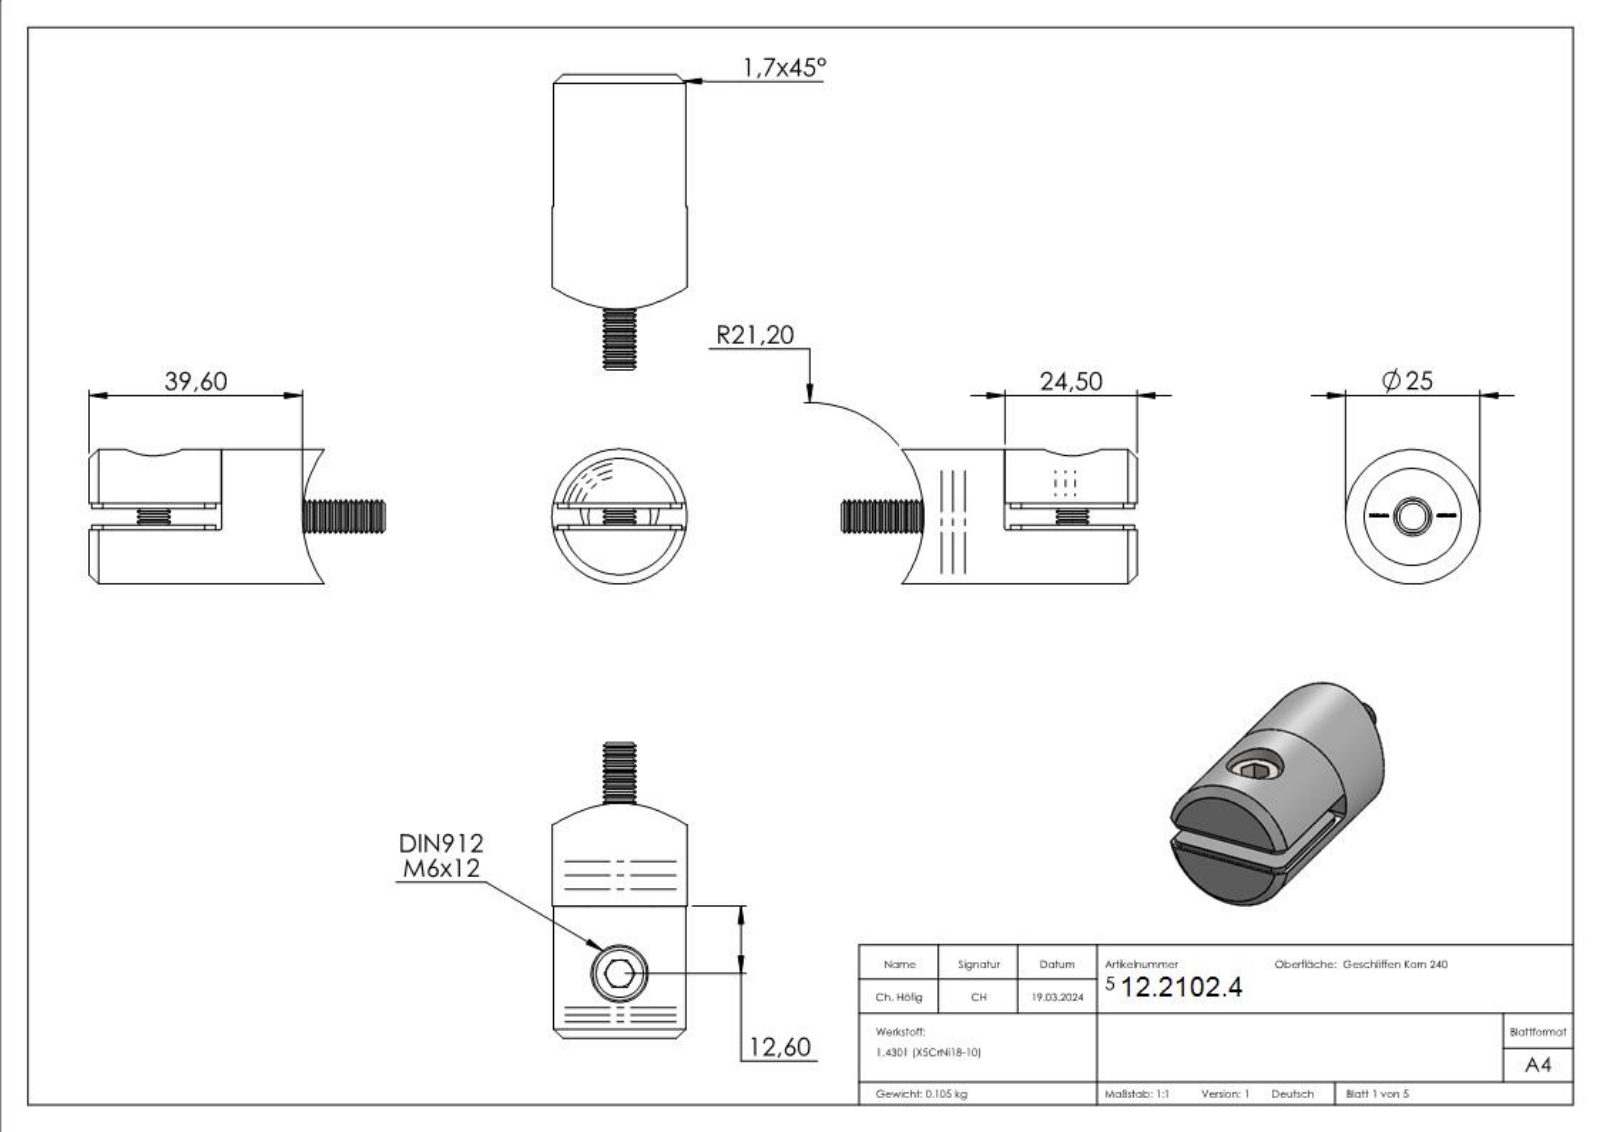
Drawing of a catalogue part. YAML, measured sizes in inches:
part_name: "socket head cap screw_din_DIN 912 M6 x 12 --- 12S; 5533X-240 Teil1_55336-240 Teil1; 55336-240; socket countersunk head screw_din_DIN 7991 - M6 x 25 --- 25S (+2 more)"
step_written_by: "SolidWorks 2018 (CONFIG_CONTROL_DESIGN)"
units: inches
bodies: {solids: 6, faces: 715, planar: 213, cylindrical: 187, other: 315}
overall_size: [2.161, 0.984, 0.984]
volume: 0.942
surface_area: 16.36
round_holes:
  - {diameter: 0.157, count: 2}
  - {diameter: 0.197, count: 1}
  - {diameter: 0.256, count: 1}
  - {diameter: 0.276, count: 1}
  - {diameter: 0.28, count: 1}
  - {diameter: 0.417, count: 1}
  - {diameter: 0.575, count: 1}
  - {diameter: 0.709, count: 1}
round_bosses_or_shafts:
  - {diameter: 0.236, count: 2}
  - {diameter: 0.984, count: 1}
  - {diameter: 0.456, count: 1}
  - {diameter: 0.394, count: 1}
partial_cylinders:
  - {radius: 0.008, count: 40}
  - {radius: 0.079, count: 6}
  - {radius: 0.049, count: 2}
  - {radius: 0.02, count: 1}
  - {radius: 0.835, count: 1}
face_to_face_distances: [0.157, 0.039, 0.197, 0.118, 1.358, 0.394, 0.965, 0.236, 0.39, 0.969]
hole_center_spacings: [0.369, 0.472]
